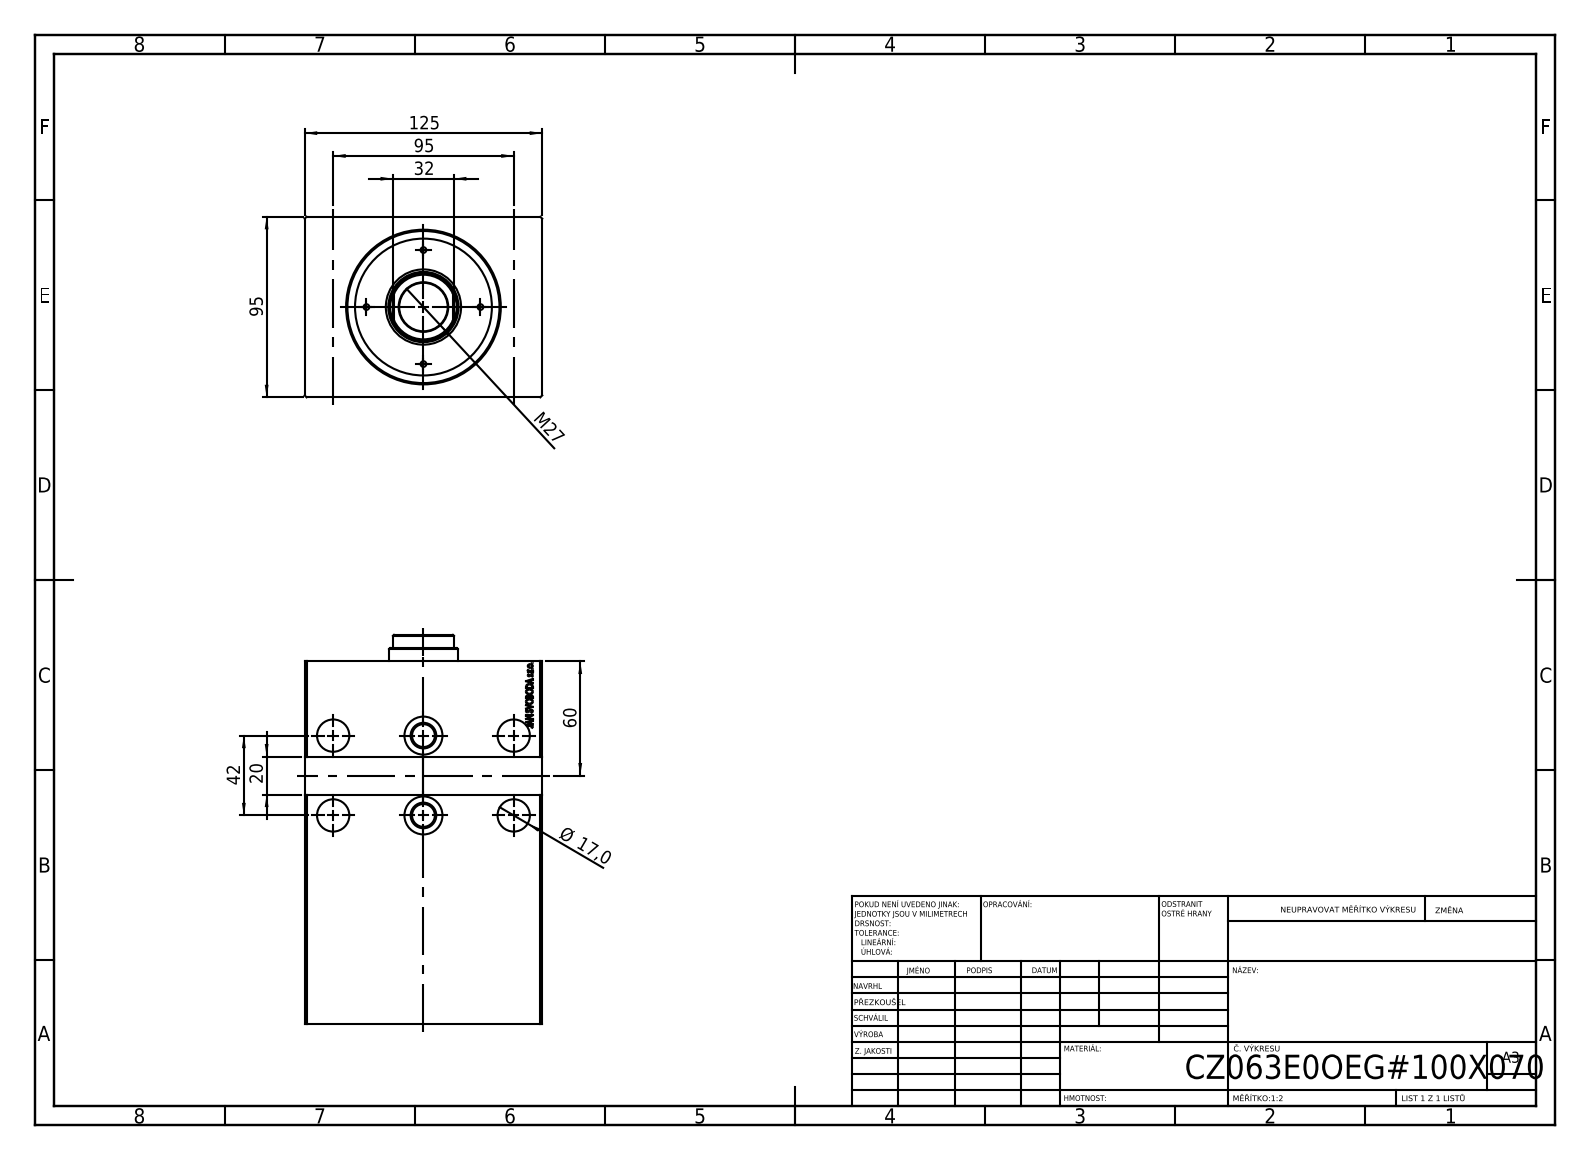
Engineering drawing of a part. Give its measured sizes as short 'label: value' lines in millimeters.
written by: SolidWorks 2019 (CONFIG_CONTROL_DESIGN)
unit: mm
bodies: 1 solid, 805 faces (393 planar, 30 cylindrical, 382 other)
size: 191 × 125 × 95
volume: 1 617 000 mm³; area: 161 445 mm²
holes: 4× ⌀17, 2× ⌀8, 2× ⌀12, 2× ⌀20, 1× ⌀36, 1× ⌀63, 1× ⌀80
bosses: 2× ⌀13.5
face distances: 95, 125, 191, 170.2, 20.8, 2, 93, 14, 156.2, 177
hole spacings: 47.5, 63.41, 42, 95, 103.87, 20.52, 27.02, 45.84
